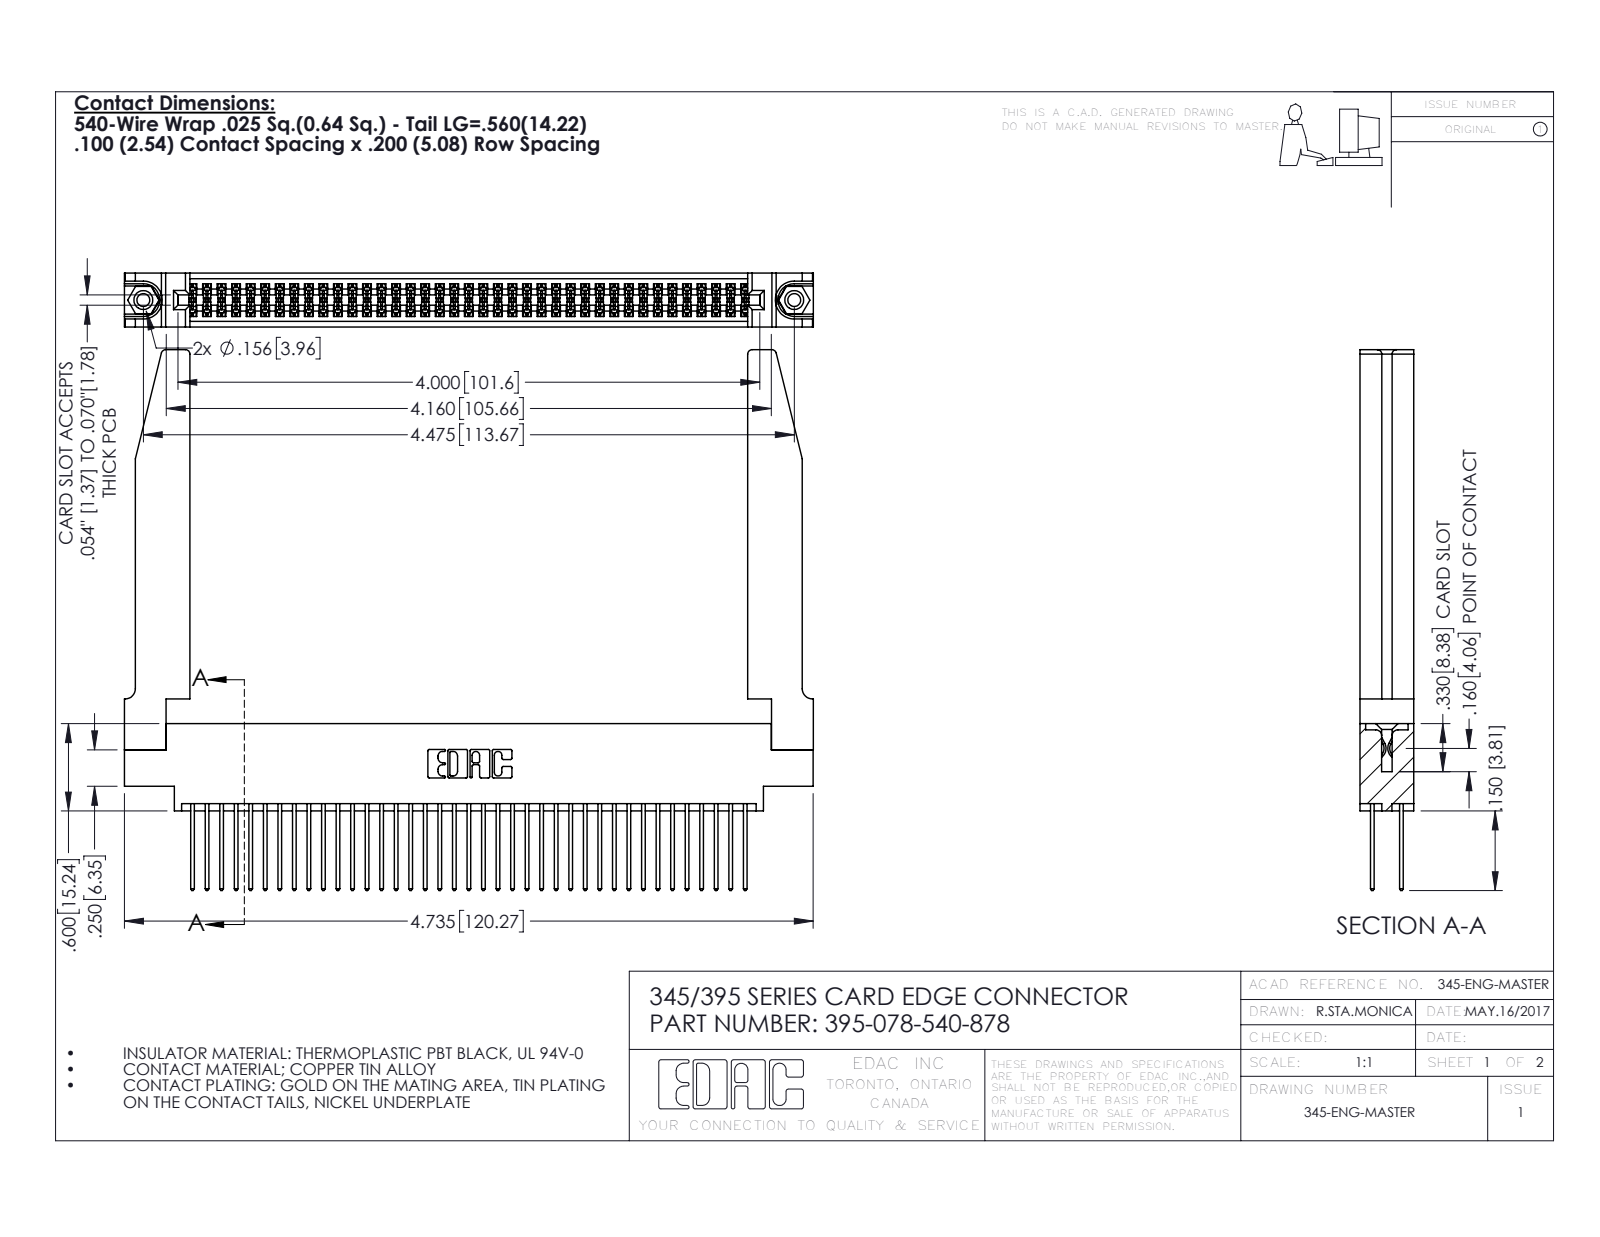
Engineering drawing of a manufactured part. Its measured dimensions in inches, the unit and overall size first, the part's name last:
Units: inches
Overall size (bounding box): 4.736 × 3.717 × 0.37
Round holes (diameter × count): ⌀0.089 ×2, ⌀0.125 ×2, ⌀0.156 ×2, ⌀0.064 ×1
Round bosses / shafts (diameter × count): ⌀0.155 ×2
Partial cylindrical surfaces — rounded edges, fillets, slot ends (radius × count): R0.006 ×117, R0.01 ×78, R0.01 ×22, R0.03 ×8, R0.007 ×6, R0.031 ×6, R0.026 ×3, R0.014 ×2
Main face-to-face distances: 0.072, 0.298, 0.37, 0.2, 0.098, 0.272, 0.025, 0.225, 0.175, 0.148
Hole centre spacings: 0.27, 4.239, 4.475
Volume: 1.197 in³ · Surface area: 39.99 in²
Bodies: 83 solids, 4264 faces (2800 planar, 1412 cylindrical, 52 other)
Part name (STEP PRODUCT): 345-220-078_345-220-078; 345-292-001_345-293-140; 345 Part_0.170 Offset - 0.156 Dia-TH; 345-250-001_345-250-001-102 (+1 more)
STEP written by: SolidWorks 2016 (CONFIG_CONTROL_DESIGN)
